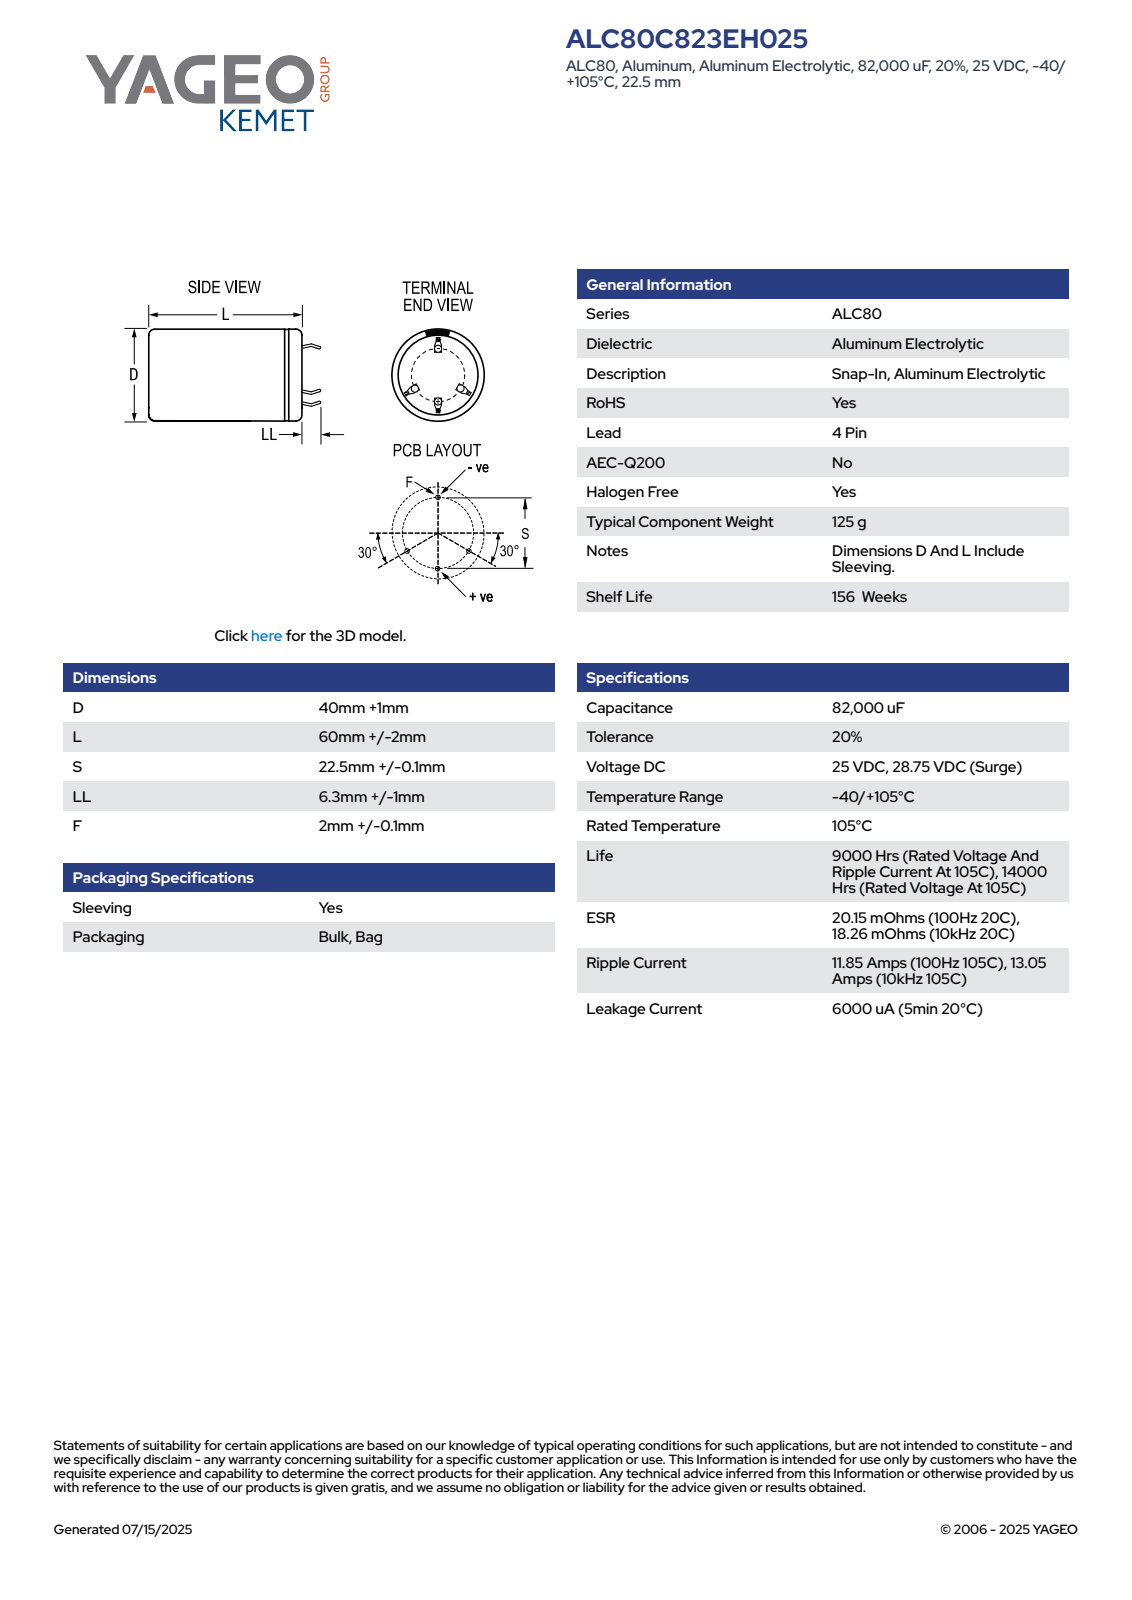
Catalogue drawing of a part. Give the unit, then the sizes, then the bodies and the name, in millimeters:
Units: millimetres
Overall size (bounding box): 69.29 × 41 × 41
Round holes (diameter × count): ⌀36.28 ×1
Round bosses / shafts (diameter × count): ⌀41 ×1
Partial cylindrical surfaces — rounded edges, fillets, slot ends (radius × count): R20.49 ×1
Main face-to-face distances: 61.99, 62.49, 0.5, 0.37, 0.6, 19.2, 0.75, 1.35, 18.83, 19.57
Volume: 81 084 mm³ · Surface area: 10 675 mm²
Bodies: 1 solid, 134 faces (80 planar, 15 cylindrical, 39 other)
Part name (STEP PRODUCT): CARS_K4P_40X60_D41L62S22.5LL7.3F2.1
STEP written by: SolidWorks 2014 (AUTOMOTIVE_DESIGN)
